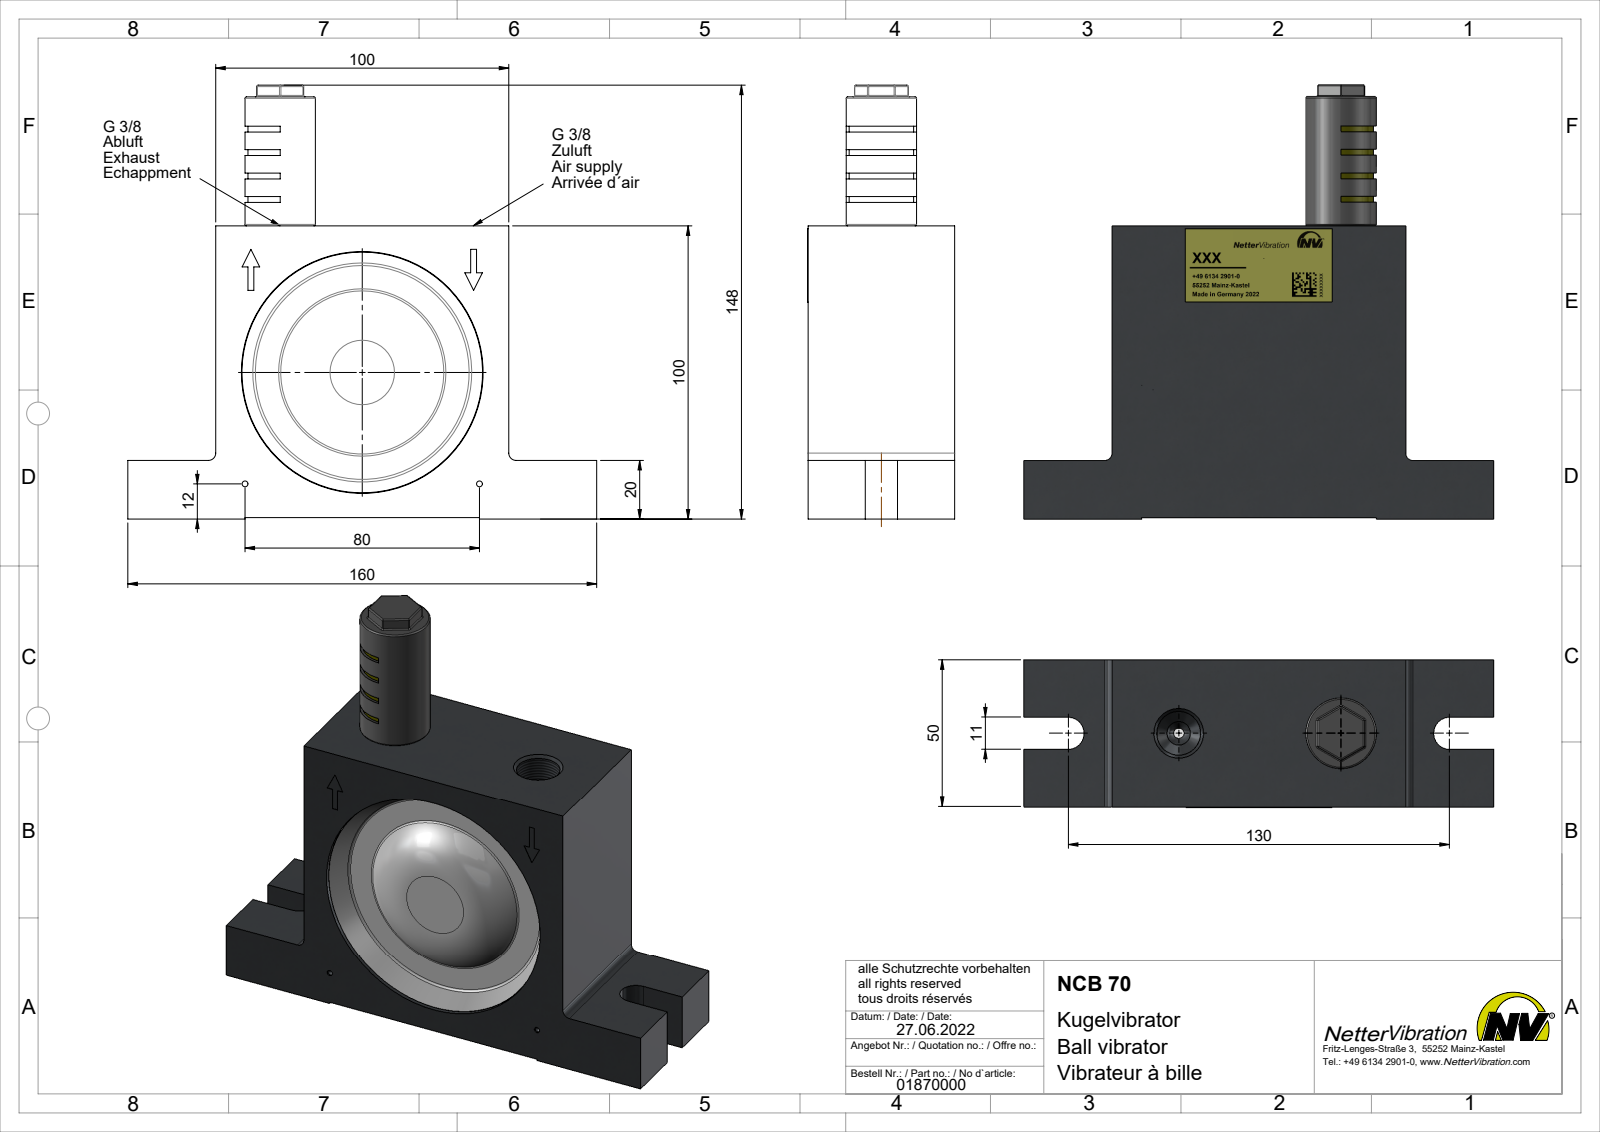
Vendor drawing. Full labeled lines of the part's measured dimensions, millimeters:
Part name (STEP PRODUCT): NCB 70 Kugelvibrator #01870000
STEP written by: SolidWorks 2015 (AUTOMOTIVE_DESIGN)
Units: millimetres
Bodies: 3 solids, 218 faces (106 planar, 47 cylindrical, 65 other)
Overall size (bounding box): 160 × 148 × 50.25
Volume: 516 521 mm³ · Surface area: 71 520 mm²
Round holes (diameter × count): ⌀2 ×2, ⌀14.95 ×2, ⌀80 ×1, ⌀82.5 ×1
Round bosses / shafts (diameter × count): ⌀24 ×1, ⌀16.66 ×1
Partial cylindrical surfaces — rounded edges, fillets, slot ends (radius × count): R0.5 ×18, R2.5 ×2, R5.5 ×2, R11 ×1
Main face-to-face distances: 100, 50, 10, 40, 99.5, 0.5, 19.5, 20, 80, 42.75
Hole centre spacings: 55.17, 55.3, 80
